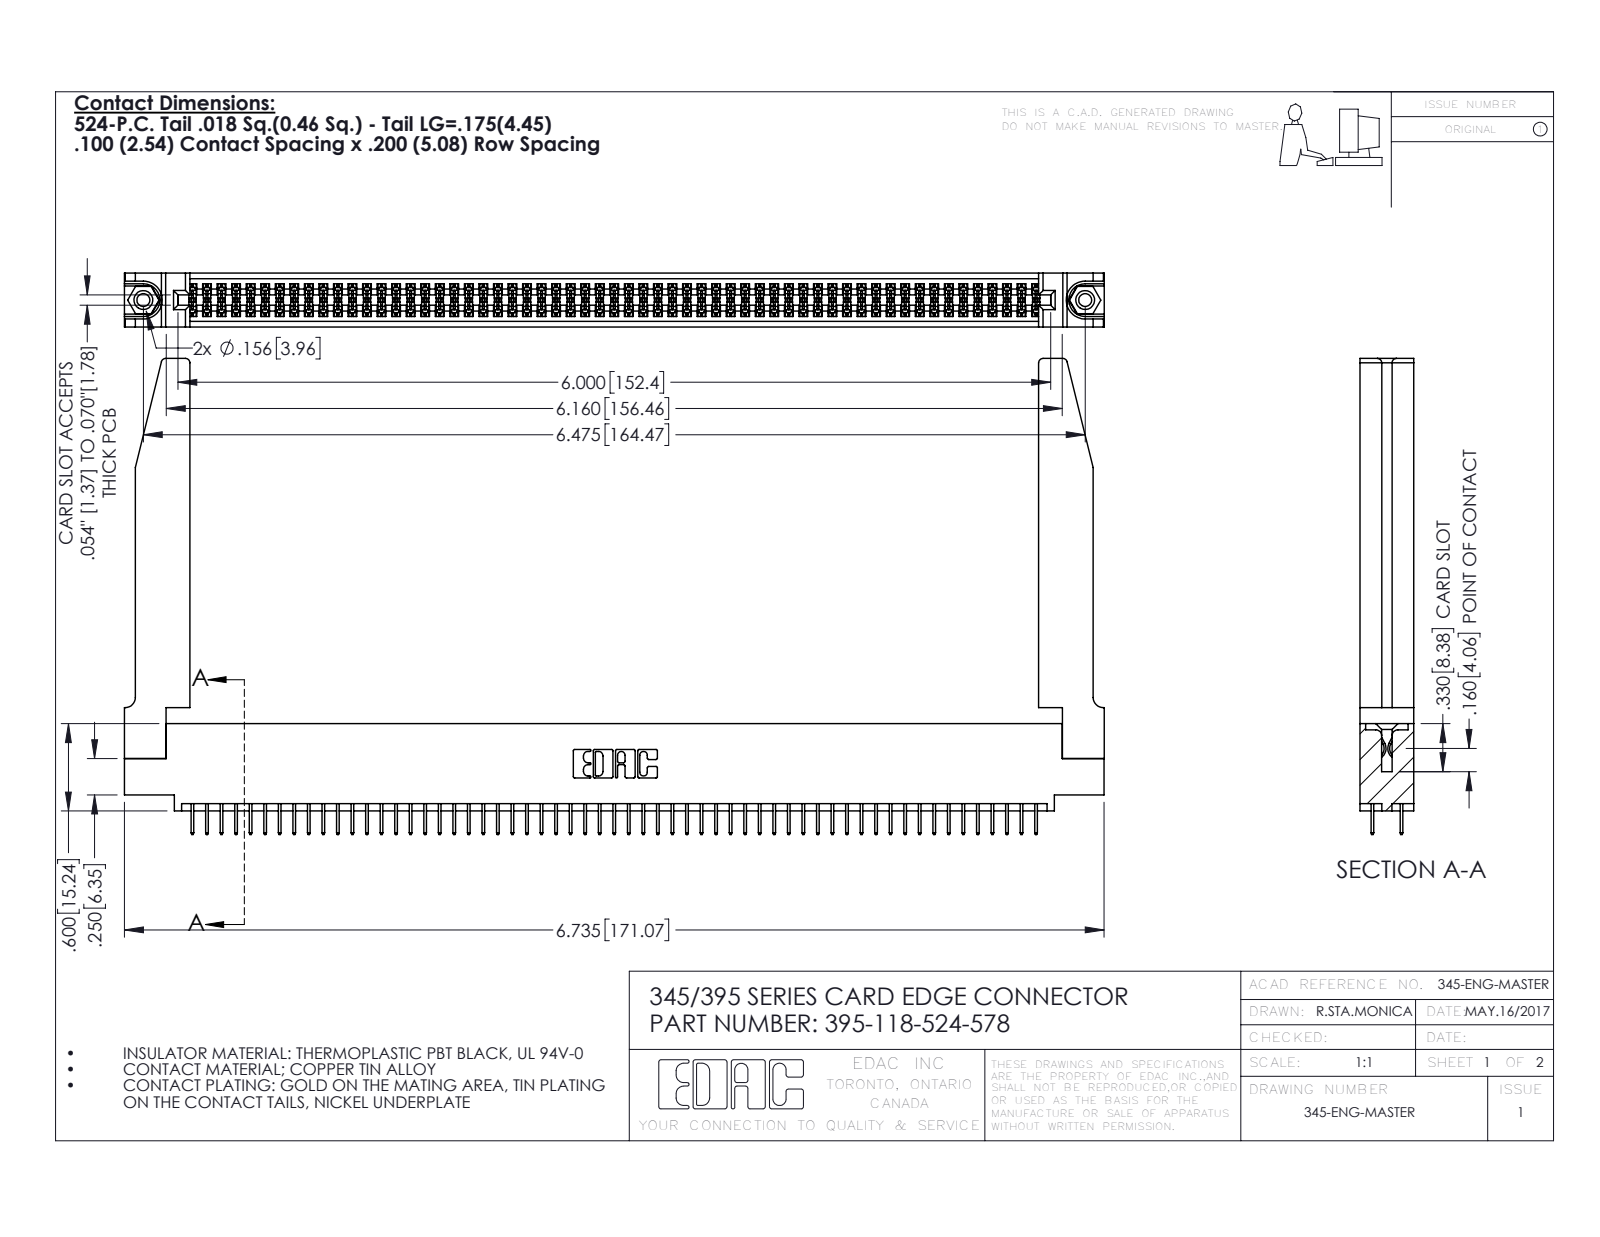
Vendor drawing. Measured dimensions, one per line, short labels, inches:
name: 395-118-524-578; 345-220-078_345-220-078; 345 Part_0.110 Offset - 0.156 Dia-TH; 345-292-001_345-293-124 (+1 more)
written by: SolidWorks 2016 (CONFIG_CONTROL_DESIGN)
unit: in
bodies: 123 solids, 6736 faces (4828 planar, 1856 cylindrical, 52 other)
size: 6.736 × 3.272 × 0.37
volume: 1.483 in³; area: 48.39 in²
holes: 2× ⌀0.089, 2× ⌀0.125, 2× ⌀0.156, 1× ⌀0.064
bosses: 2× ⌀0.155
rounds: 177× R0.006, 22× R0.01, 8× R0.03, 6× R0.007, 6× R0.031, 3× R0.026, 2× R0.014, 2× R0.019
face distances: 0.072, 0.37, 0.298, 0.2, 0.098, 0.272, 0.025, 0.225, 0.072, 0.175
hole spacings: 0.27, 6.239, 6.475
